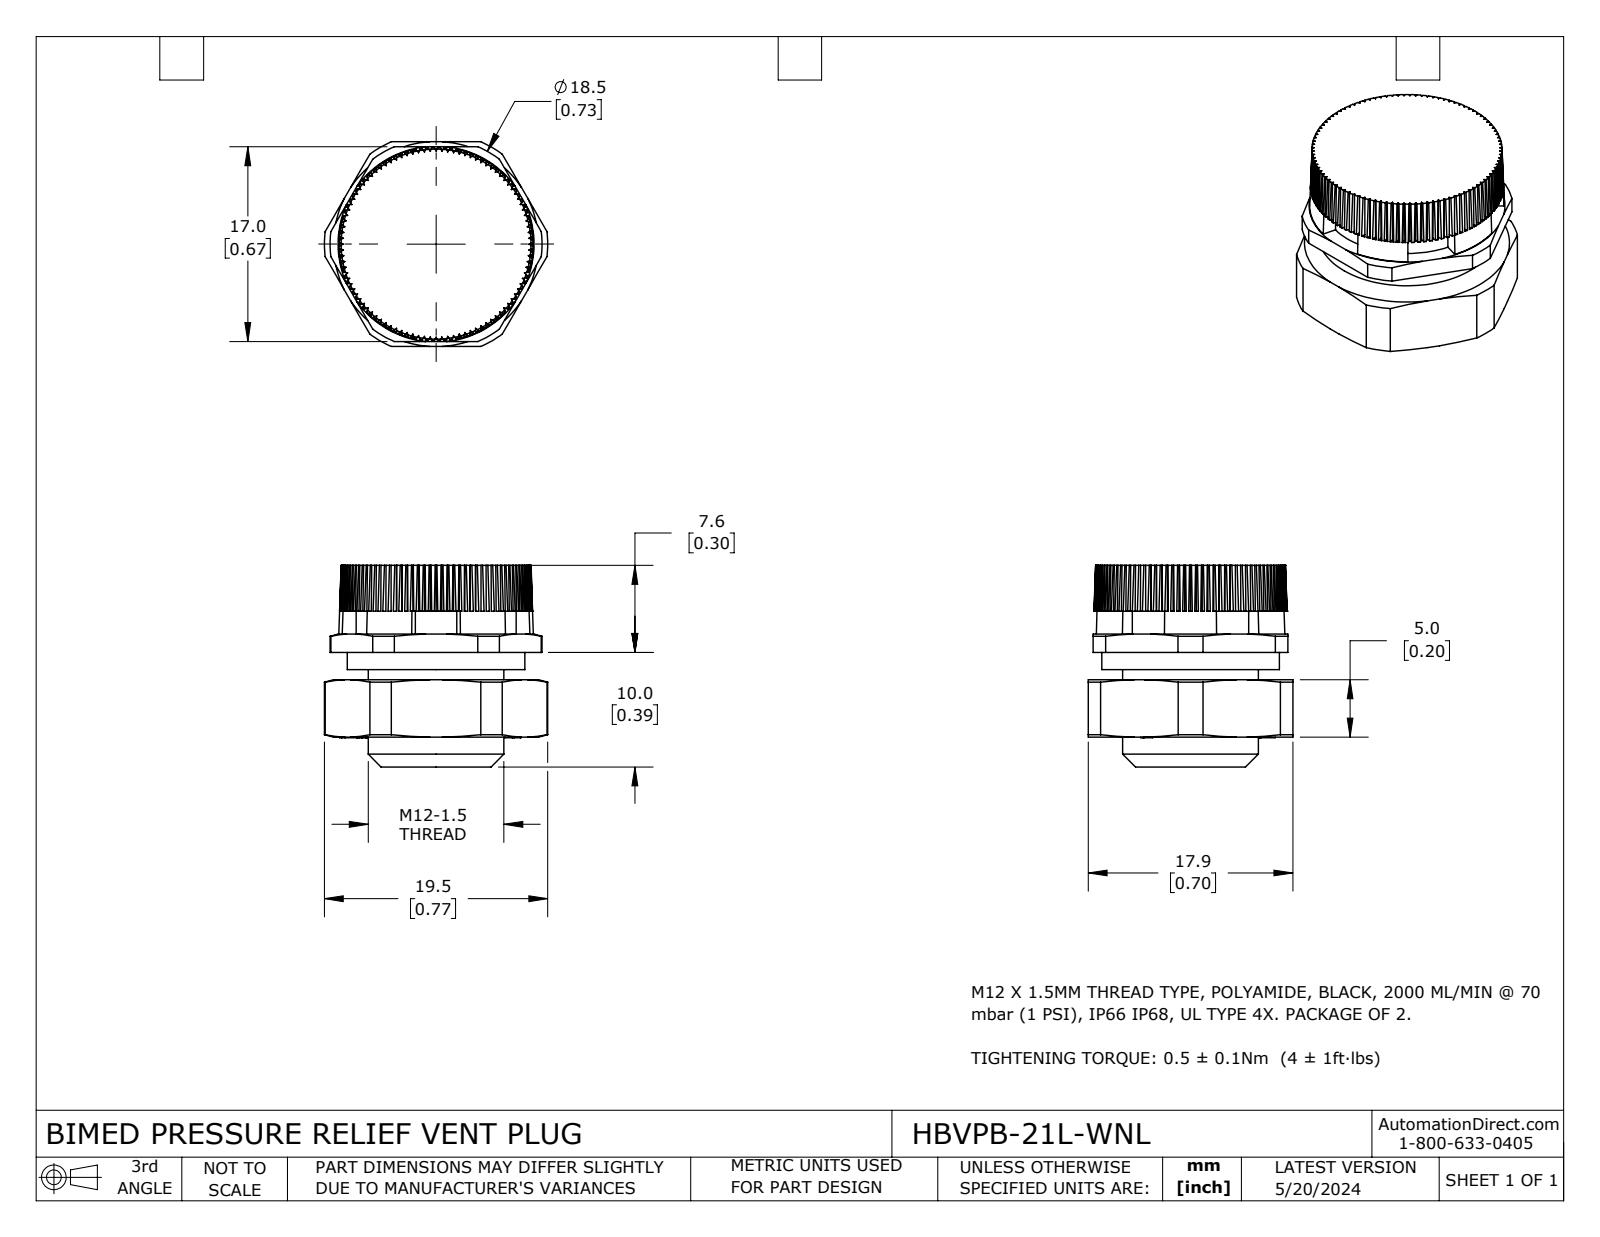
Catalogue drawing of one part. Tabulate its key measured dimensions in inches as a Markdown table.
| quantity | value |
| --- | --- |
| part name | HBVPB-21L-WNL |
| STEP written by | SolidWorks 2023 (CONFIG_CONTROL_DESIGN) |
| units | inches |
| bodies | 2 solids, 480 faces (357 planar, 29 cylindrical, 94 other) |
| overall size | 0.768 × 0.703 × 0.693 |
| volume | 0.198 in³ |
| surface area | 4.006 in² |
| round holes (diameter × count) | 0.276 × 1, 0.472 × 1, 0.492 × 1 |
| round bosses / shafts (diameter × count) | 0.61 × 1, 0.467 × 1 |
| partial cylindrical surfaces (radius × count) | 0.285 × 1, 0.364 × 1, 0.384 × 1 |
| main face-to-face distances | 0.393, 0.197, 0.59, 0.703, 0.291, 0.094, 0.299, 0.281, 0.017, 0.686 |
